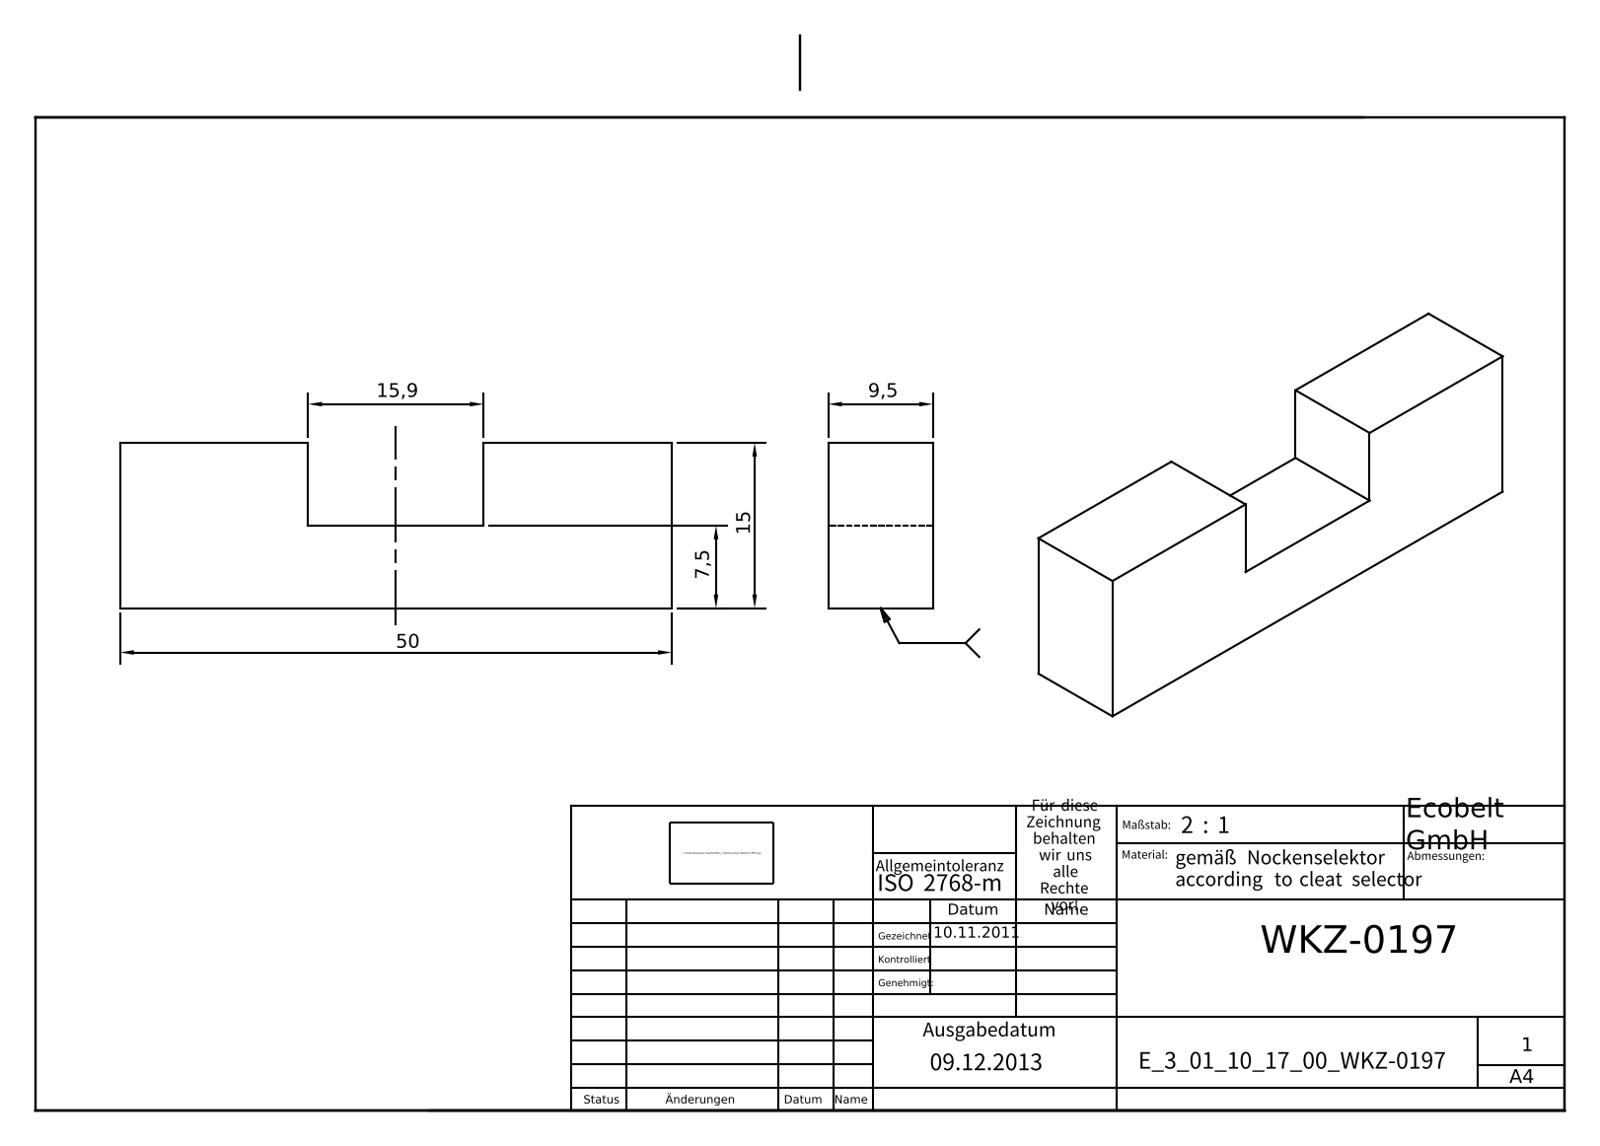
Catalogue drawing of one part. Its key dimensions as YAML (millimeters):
part_name: "E_3_01_10_17_00_WKZ-0197"
step_written_by: "Autodesk Inventor 2025 (AUTOMOTIVE_DESIGN)"
units: millimeters
bodies: {solids: 1, faces: 10, planar: 10, cylindrical: 0, other: 0}
overall_size: [50, 15, 9.5]
volume: 5992
surface_area: 2639
face_to_face_distances: [9.5, 15, 7.5, 17.05, 32.95, 50, 15.9]
